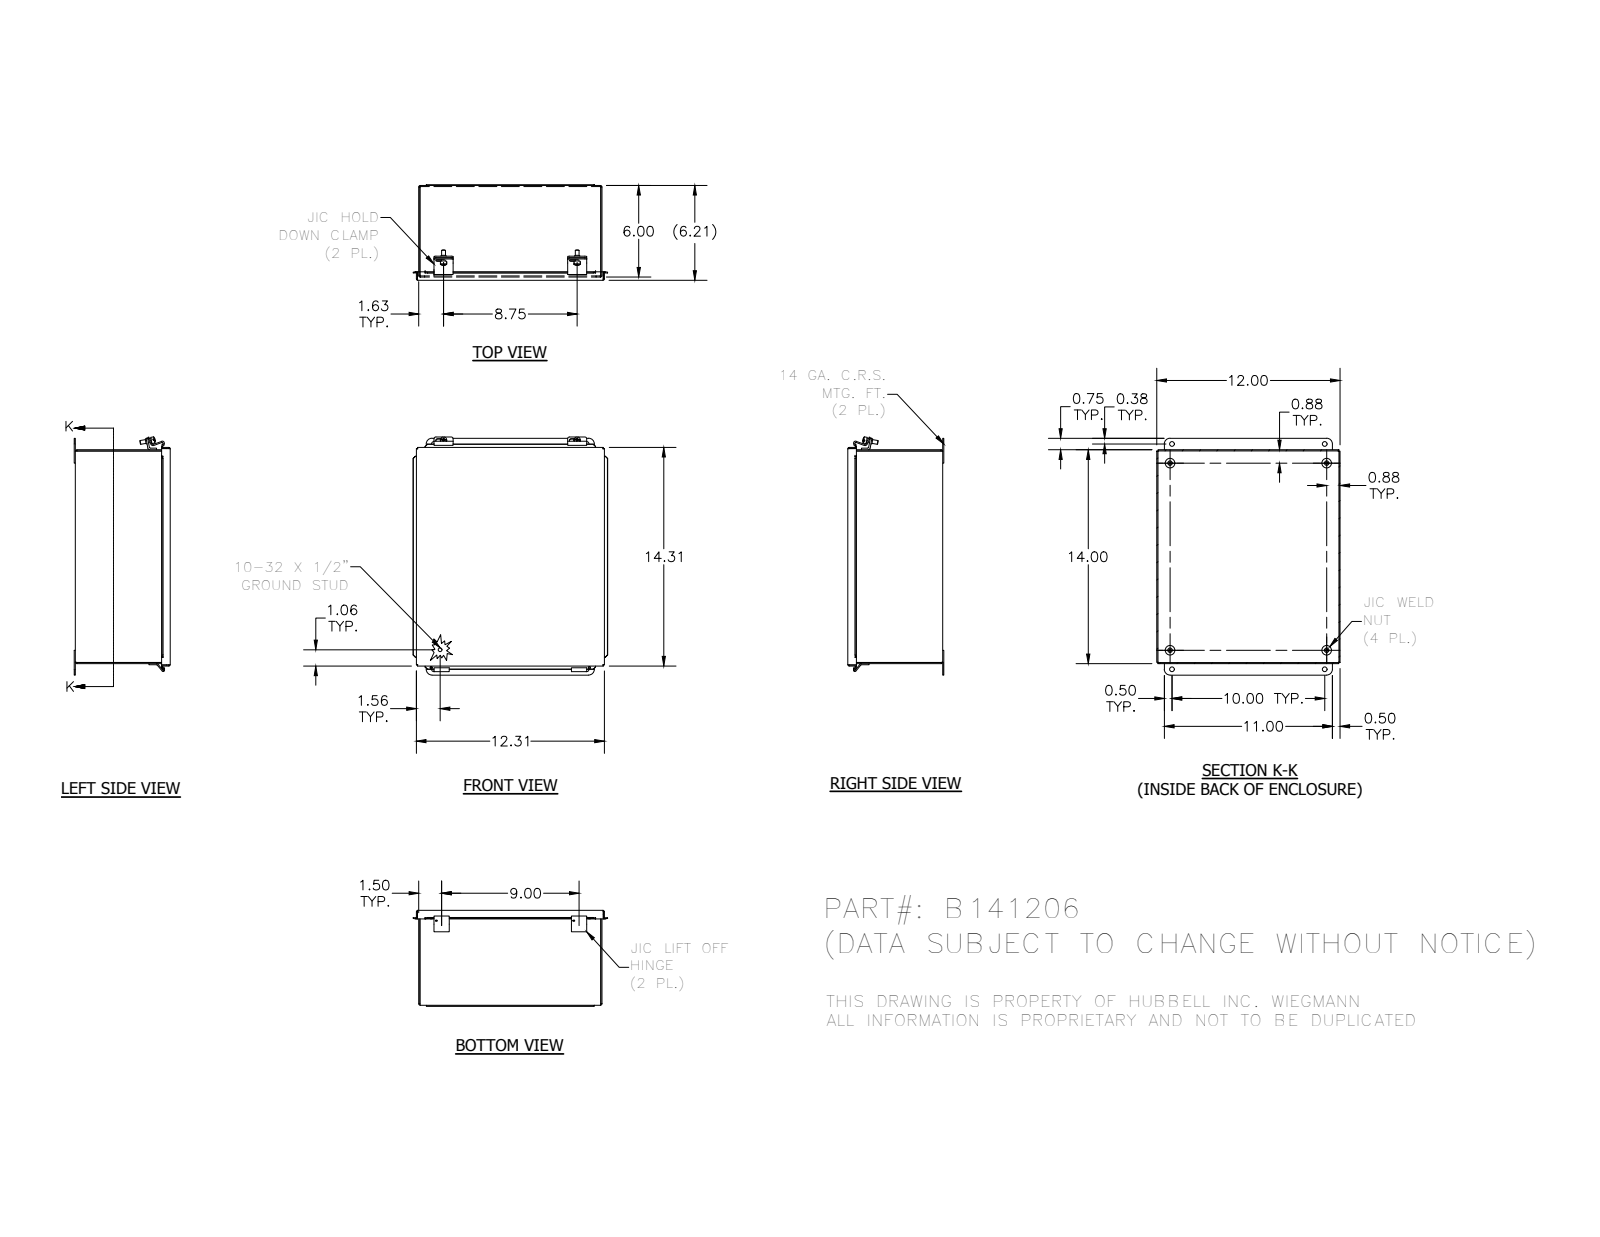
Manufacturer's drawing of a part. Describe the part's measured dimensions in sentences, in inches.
The part is named "B141206; 3499; 3485; C1001 (+7 more)". Its 3-D file was written by "Autodesk Inventor 2012 (AUTOMOTIVE_DESIGN)". It is 19 solids with 422 faces: 279 planar, 98 cylindrical and 45 other. Overall it measures 15.593 by 12.739 by 6.287 inches. Its volume is 58.55 cubic inches and its surface area 1 587 square inches. Round holes: 4 of diameter 0.156, 4 of diameter 0.31, 2 of diameter 0.125, 2 of diameter 0.14, 2 of diameter 0.196. Round bosses or shafts: 4 of diameter 0.625, 4 of diameter 0.3, 3 of diameter 0.25, 2 of diameter 0.41, 2 of diameter 0.344, 1 of diameter 0.19. Partial cylindrical surfaces (rounded edges, fillets, slot ends): 16 of radius 0.031, 8 of radius 0.093, 8 of radius 0.105, 8 of radius 0.125, 4 of radius 0.133, 4 of radius 0.375, 3 of radius 0.063, 3 of radius 0.126. The main face-to-face distances are 0.074, 6.15, 0.062, 6.212, 6.076, 6.138, 11.926, 13.926, 12, 11.852. The hole center spacings are 1.256, 10, 10.202, 10.202, 10.25, 12.25, 13.5, 14.801.
